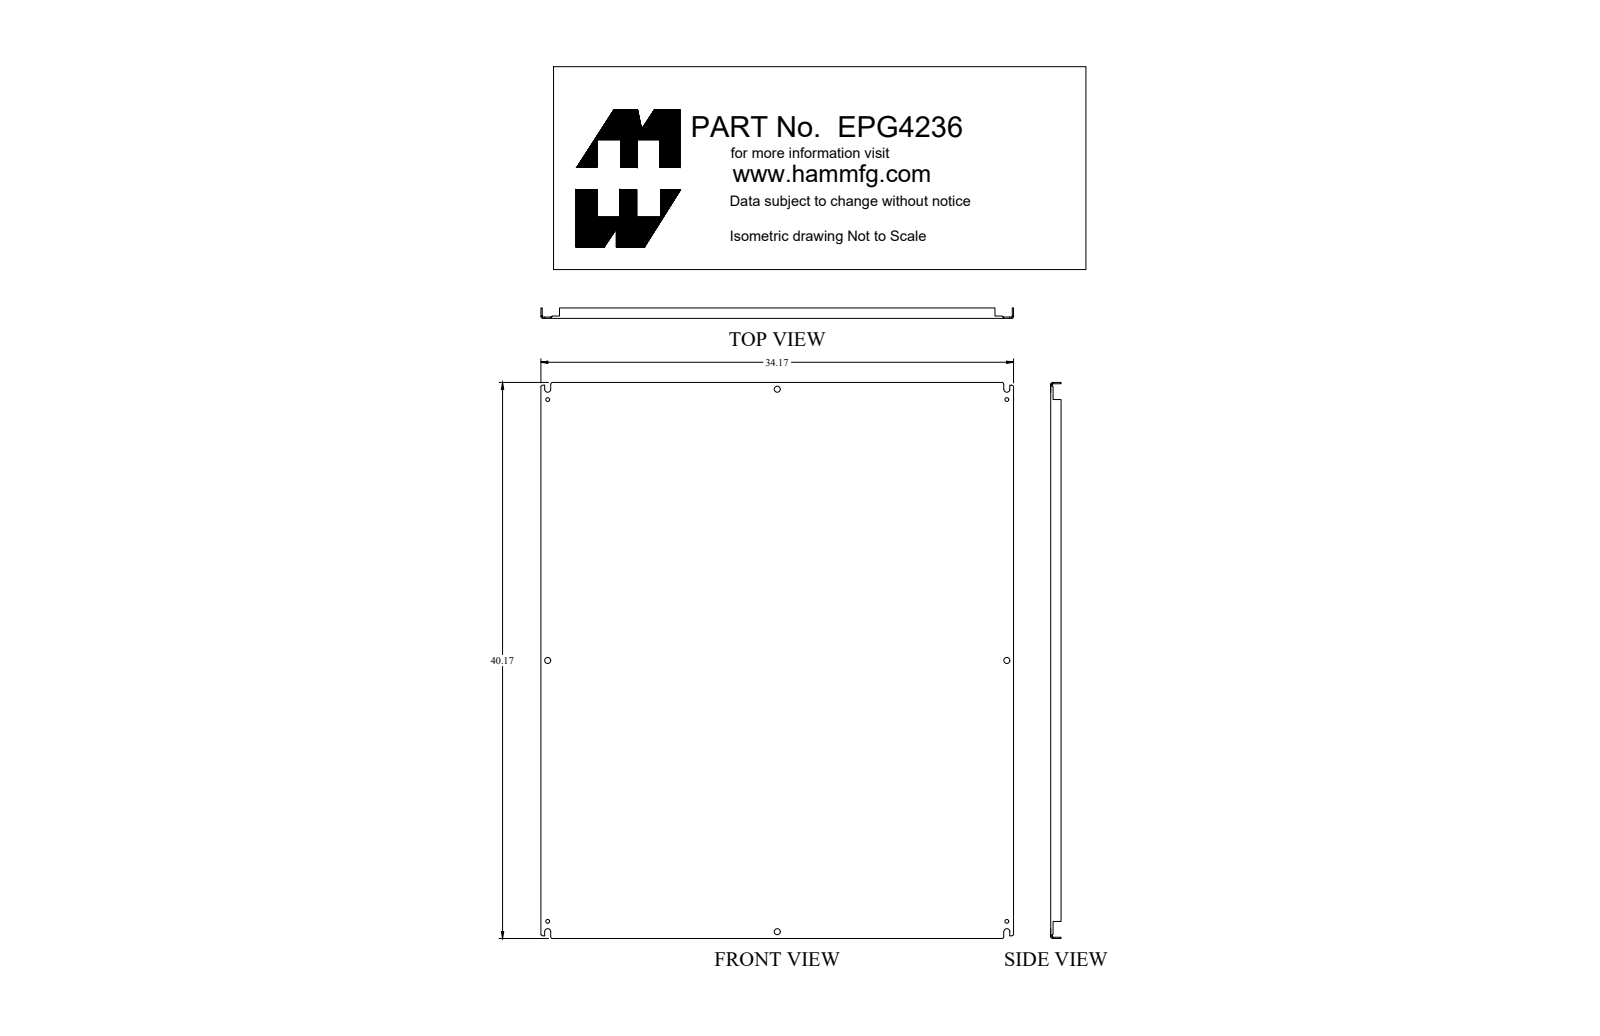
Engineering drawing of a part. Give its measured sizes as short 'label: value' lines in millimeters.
name: EPG4236
written by: SolidWorks 2018 (AUTOMOTIVE_DESIGN)
unit: mm
bodies: 1 solid, 136 faces (74 planar, 46 cylindrical, 16 other)
size: 1020.3 × 867.9 × 19.1
volume: 2 266 000 mm³; area: 1 888 000 mm²
holes: 4× ⌀7.1, 4× ⌀11.1
rounds: 4× R1.2, 4× R1.6, 4× R3.6, 4× R5.6
face distances: 2.4, 865.5, 1017.9, 863.1, 867.9, 1015.5, 1020.3, 19.1, 16.6, 4.3
hole spacings: 421.9, 478.6, 652.2, 969.4, 1063.4, 843, 957.3, 1275.5
